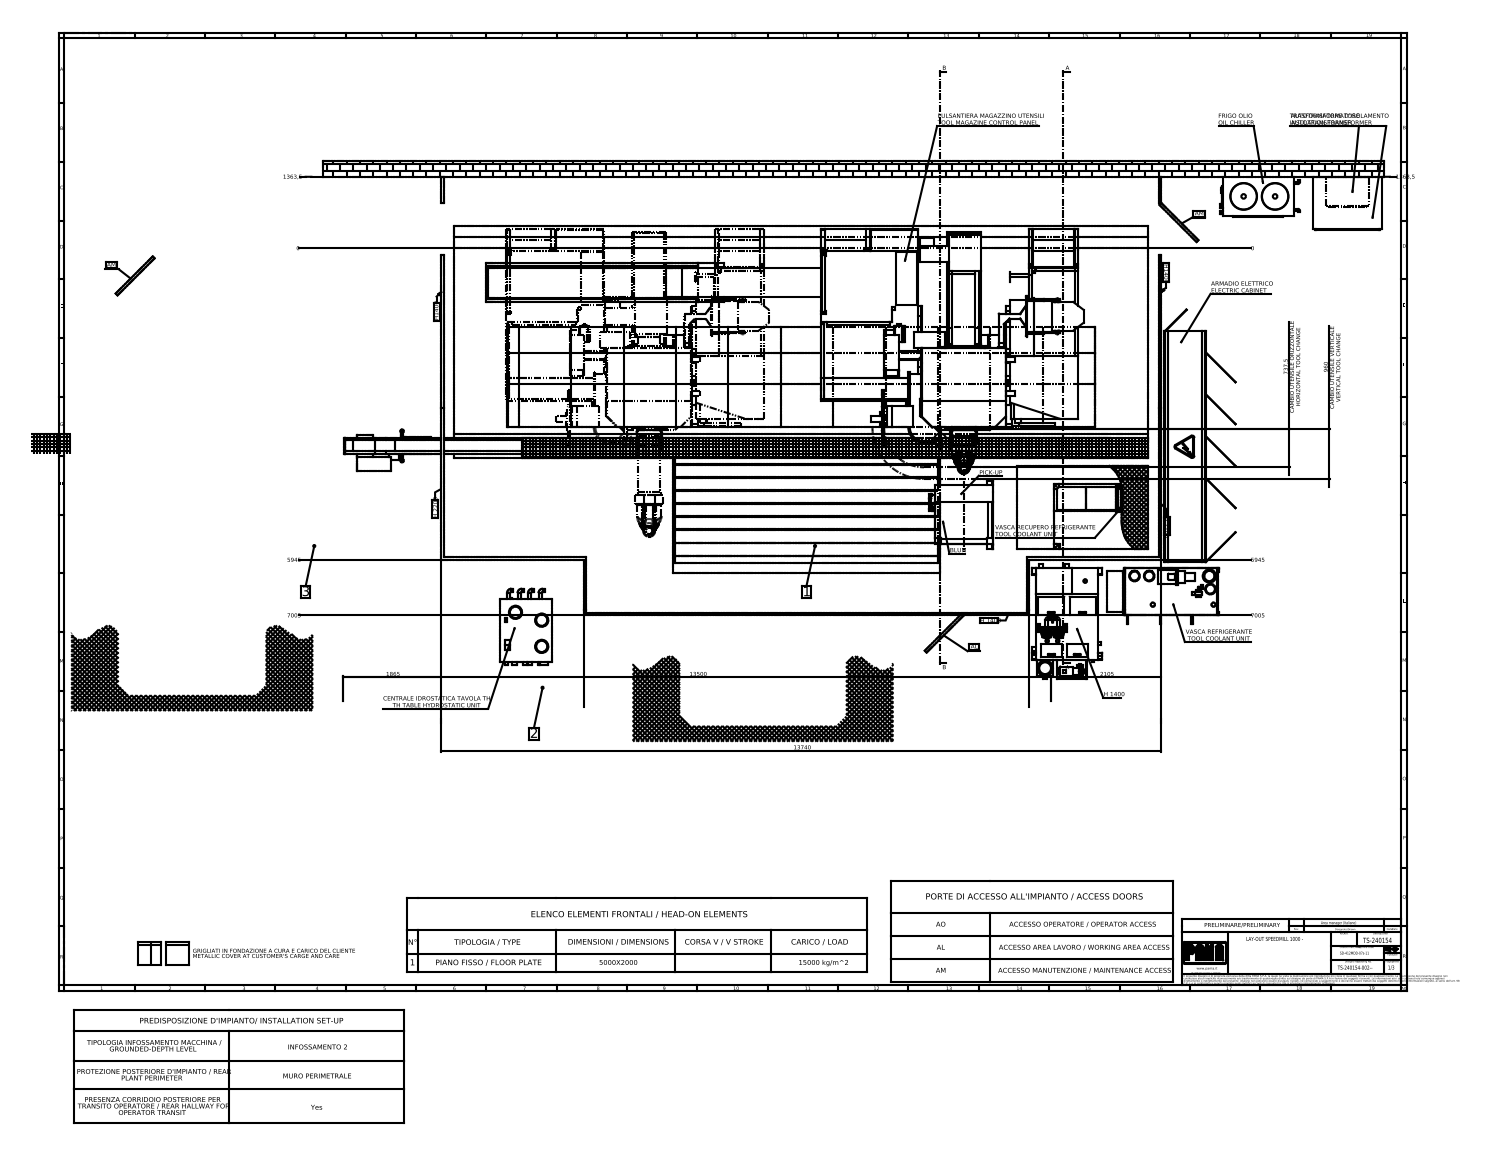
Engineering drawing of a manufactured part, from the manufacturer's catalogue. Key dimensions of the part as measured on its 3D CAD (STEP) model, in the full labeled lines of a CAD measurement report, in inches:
Part name (STEP PRODUCT): S002770_L=8000; S003509_BORING - CORTA; S000887; S001568_1000 L (+8 more)
STEP written by: SolidWorks 2023 (AUTOMOTIVE_DESIGN)
Units: inches
Bodies: 390 solids, 6138 faces (4246 planar, 1310 cylindrical, 582 other)
Overall size (bounding box): 952.642 × 457.421 × 370.079
Volume: 30 050 000 in³ · Surface area: 2 620 000 in²
Round holes (diameter × count): ⌀1.378 ×64, ⌀2.74 ×63, ⌀0.512 ×8, ⌀0.551 ×8, ⌀0.315 ×6, ⌀1.26 ×6, ⌀0.492 ×4, ⌀1.969 ×3, ⌀2.231 ×3, ⌀0.165 ×2, ⌀0.748 ×2, ⌀1.181 ×2
Round bosses / shafts (diameter × count): ⌀0.787 ×14, ⌀0.354 ×10, ⌀1.181 ×8, ⌀2.61 ×7, ⌀2.362 ×7, ⌀1.378 ×6, ⌀7.874 ×4, ⌀6.693 ×4
Partial cylindrical surfaces — rounded edges, fillets, slot ends (radius × count): R0.197 ×141, R0.591 ×46, R0.236 ×36, R0.394 ×27, R1.378 ×26, R0.787 ×19, R0.118 ×16, R0.315 ×16
Main face-to-face distances: 78.74, 11.811, 1.969, 52.756, 25.984, 457.421, 445.61, 5.906, 41.732, 796.85
Hole centre spacings: 9.843, 19.685, 29.528, 39.37, 49.213, 59.055, 68.898, 78.74
